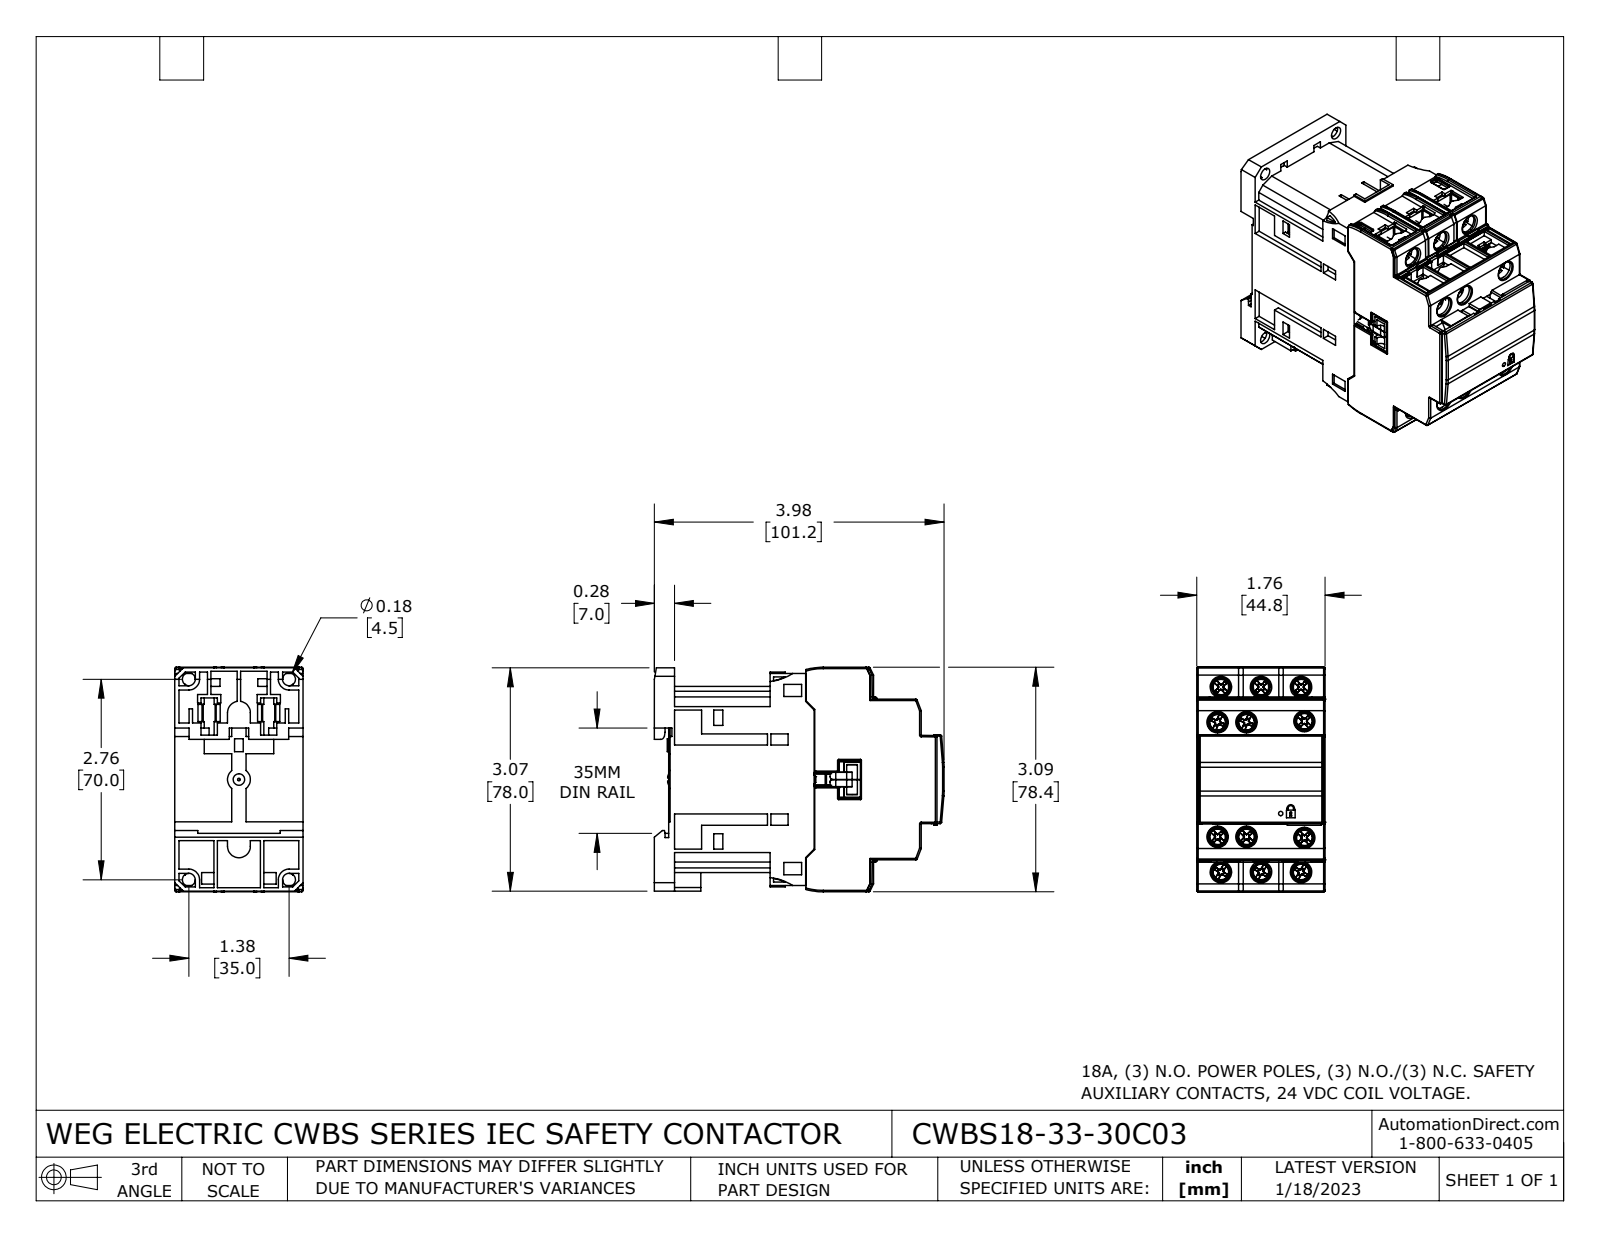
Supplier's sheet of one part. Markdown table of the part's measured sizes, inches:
| quantity | value |
| --- | --- |
| part name | CWBS18-33-30C03 |
| STEP written by | SolidWorks 2021 (CONFIG_CONTROL_DESIGN) |
| units | inches |
| bodies | 45 solids, 3244 faces (2306 planar, 594 cylindrical, 344 other) |
| overall size | 3.982 × 3.087 × 1.764 |
| volume | 15.16 in³ |
| surface area | 128.7 in² |
| round holes (diameter × count) | 0.124 × 12, 0.256 × 6, 0.177 × 4, 0.236 × 2, 0.059 × 1 |
| round bosses / shafts (diameter × count) | 0.169 × 12, 0.138 × 12, 0.107 × 8, 0.107 × 4 |
| partial cylindrical surfaces (radius × count) | 0.02 × 134, 0.012 × 52, 0.071 × 24, 0.964 × 24, 2.128 × 24, 0.016 × 20, 0.039 × 17, 0.106 × 11 |
| main face-to-face distances | 1.764, 0.047, 3.667, 1.717, 1.687, 0.028, 0.157, 1.53, 1.98, 2.138 |
| hole center spacings | 0.551, 1.102, 0.829, 2.396, 0.237, 0.398, 0.584, 0.598 |
